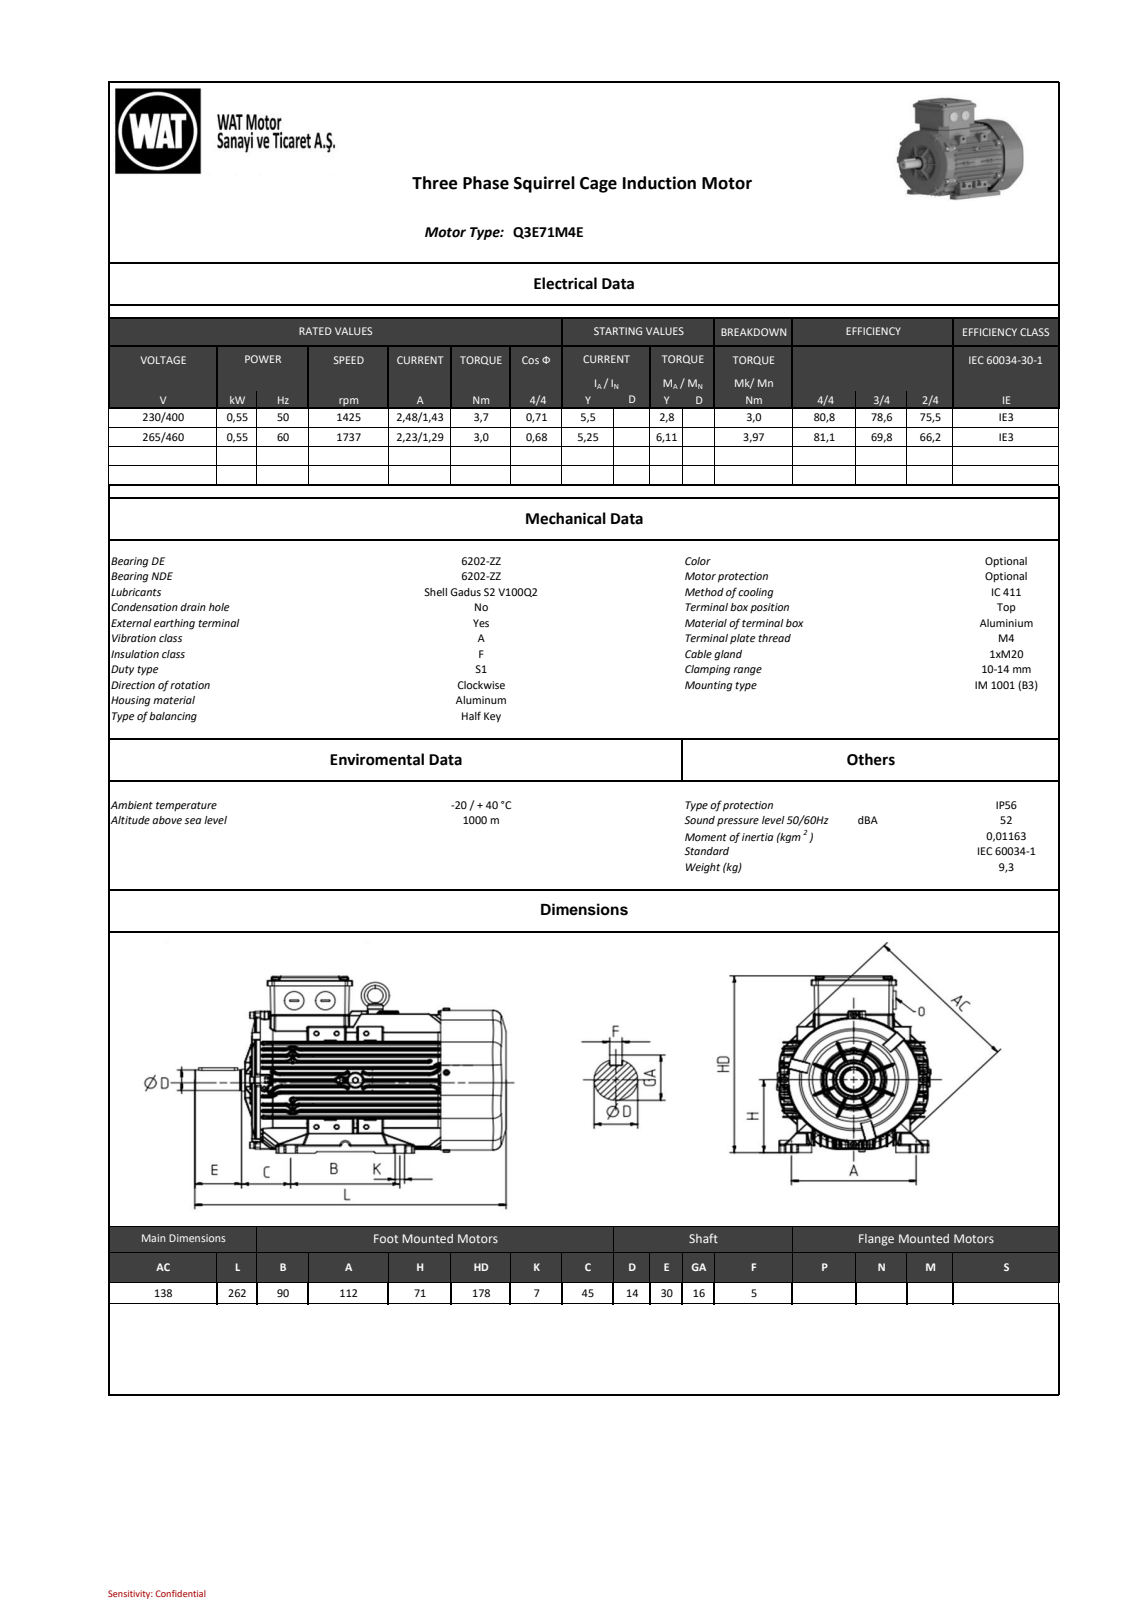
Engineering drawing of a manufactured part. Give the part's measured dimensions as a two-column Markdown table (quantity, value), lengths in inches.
| quantity | value |
| --- | --- |
| part name | 001_objects |
| STEP written by | SIEMENS PLM Software NX2206.8101 (AUTOMOTIVE_DESIGN) |
| units | inches |
| bodies | 0 solids, 2800 faces (1431 planar, 741 cylindrical, 628 other) |
| overall size | 10.315 × 7.012 × 5.433 |
| round holes (diameter × count) | 0.13 × 9, 0.144 × 8, 0.098 × 6, 0.197 × 5, 0.157 × 4, 0.177 × 4, 0.183 × 4, 0.189 × 4, 0.205 × 4, 0.276 × 4, 0.118 × 3, 0.146 × 3 |
| round bosses / shafts (diameter × count) | 0.315 × 8, 0.157 × 8, 5.433 × 1, 4.567 × 1, 4.528 × 1, 3.031 × 1, 2.402 × 1, 1.024 × 1 |
| partial cylindrical surfaces (radius × count) | 0.039 × 107, 0.02 × 54, 0.047 × 36, 0.059 × 24, 0.098 × 20, 0.157 × 17, 0.197 × 17, 0.394 × 16 |
| main face-to-face distances | 0.079, 0.118, 0.197, 0.039, 0.591, 3.268, 0.236, 0.157, 6.772, 4.331 |
| hole center spacings | 2.417, 3.442, 2.165, 1.441, 2.645, 2.646, 3.636, 2.362 |
